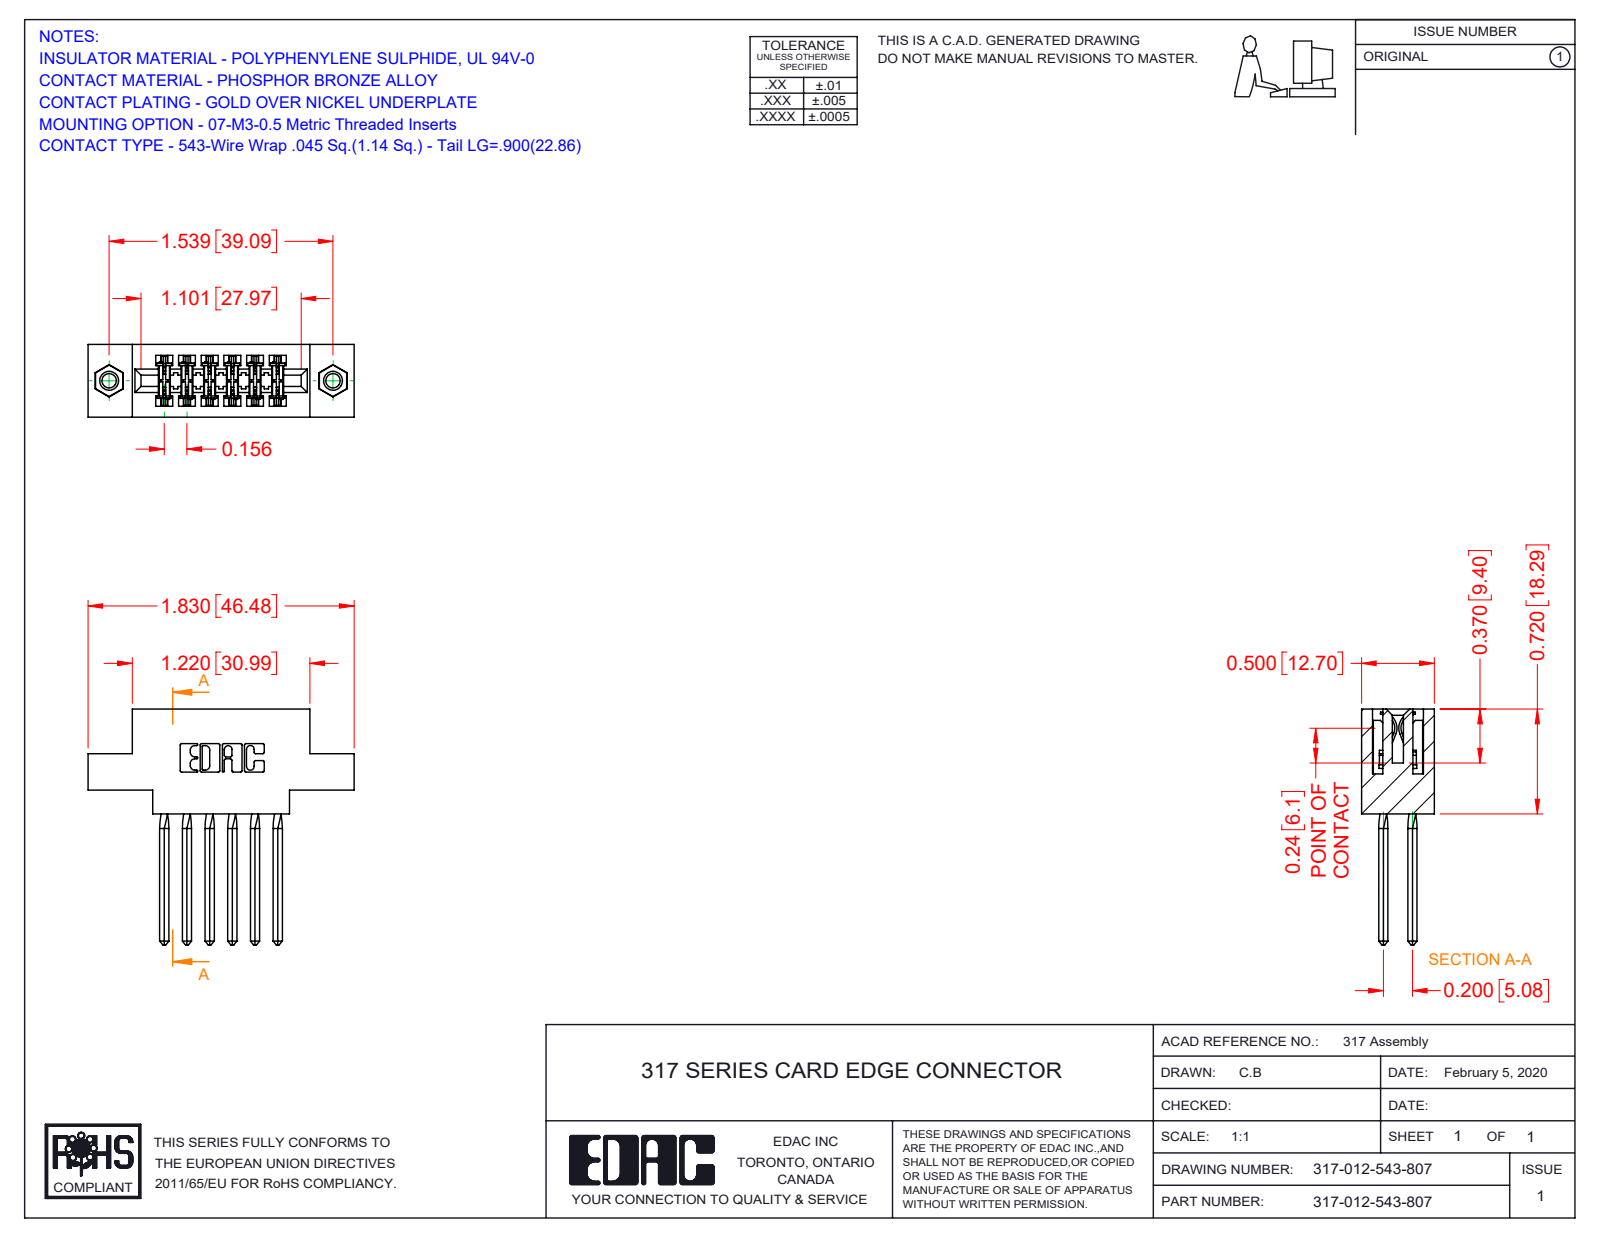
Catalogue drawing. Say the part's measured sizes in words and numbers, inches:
The part is named "317-290-001_543; 317-012-543-807; 345-250-001_345-250-005-103; 317 Part_.156 Dia - TI". Its 3-D file was written by "SolidWorks 2016 (CONFIG_CONTROL_DESIGN)". It is 15 solids with 1230 faces: 966 planar, 200 cylindrical and 64 other. Overall it measures 1.83 by 1.62 by 0.5 inches. Its volume is 0.405 cubic inches and its surface area 13.46 square inches. Round holes: 2 of diameter 0.098, 2 of diameter 0.125, 2 of diameter 0.156. Round bosses or shafts: 2 of diameter 0.155. Partial cylindrical surfaces (rounded edges, fillets, slot ends): 24 of radius 0.015, 22 of radius 0.01, 6 of radius 0.007, 6 of radius 0.031, 3 of radius 0.026, 2 of radius 0.095, 2 of radius 0.1, 2 of radius 0.11. The main face-to-face distances are 0.11, 0.5, 0.075, 0.22, 0.425, 0.065, 0.156, 0.141, 0.331, 0.116. The hole center spacings are 1.539.
